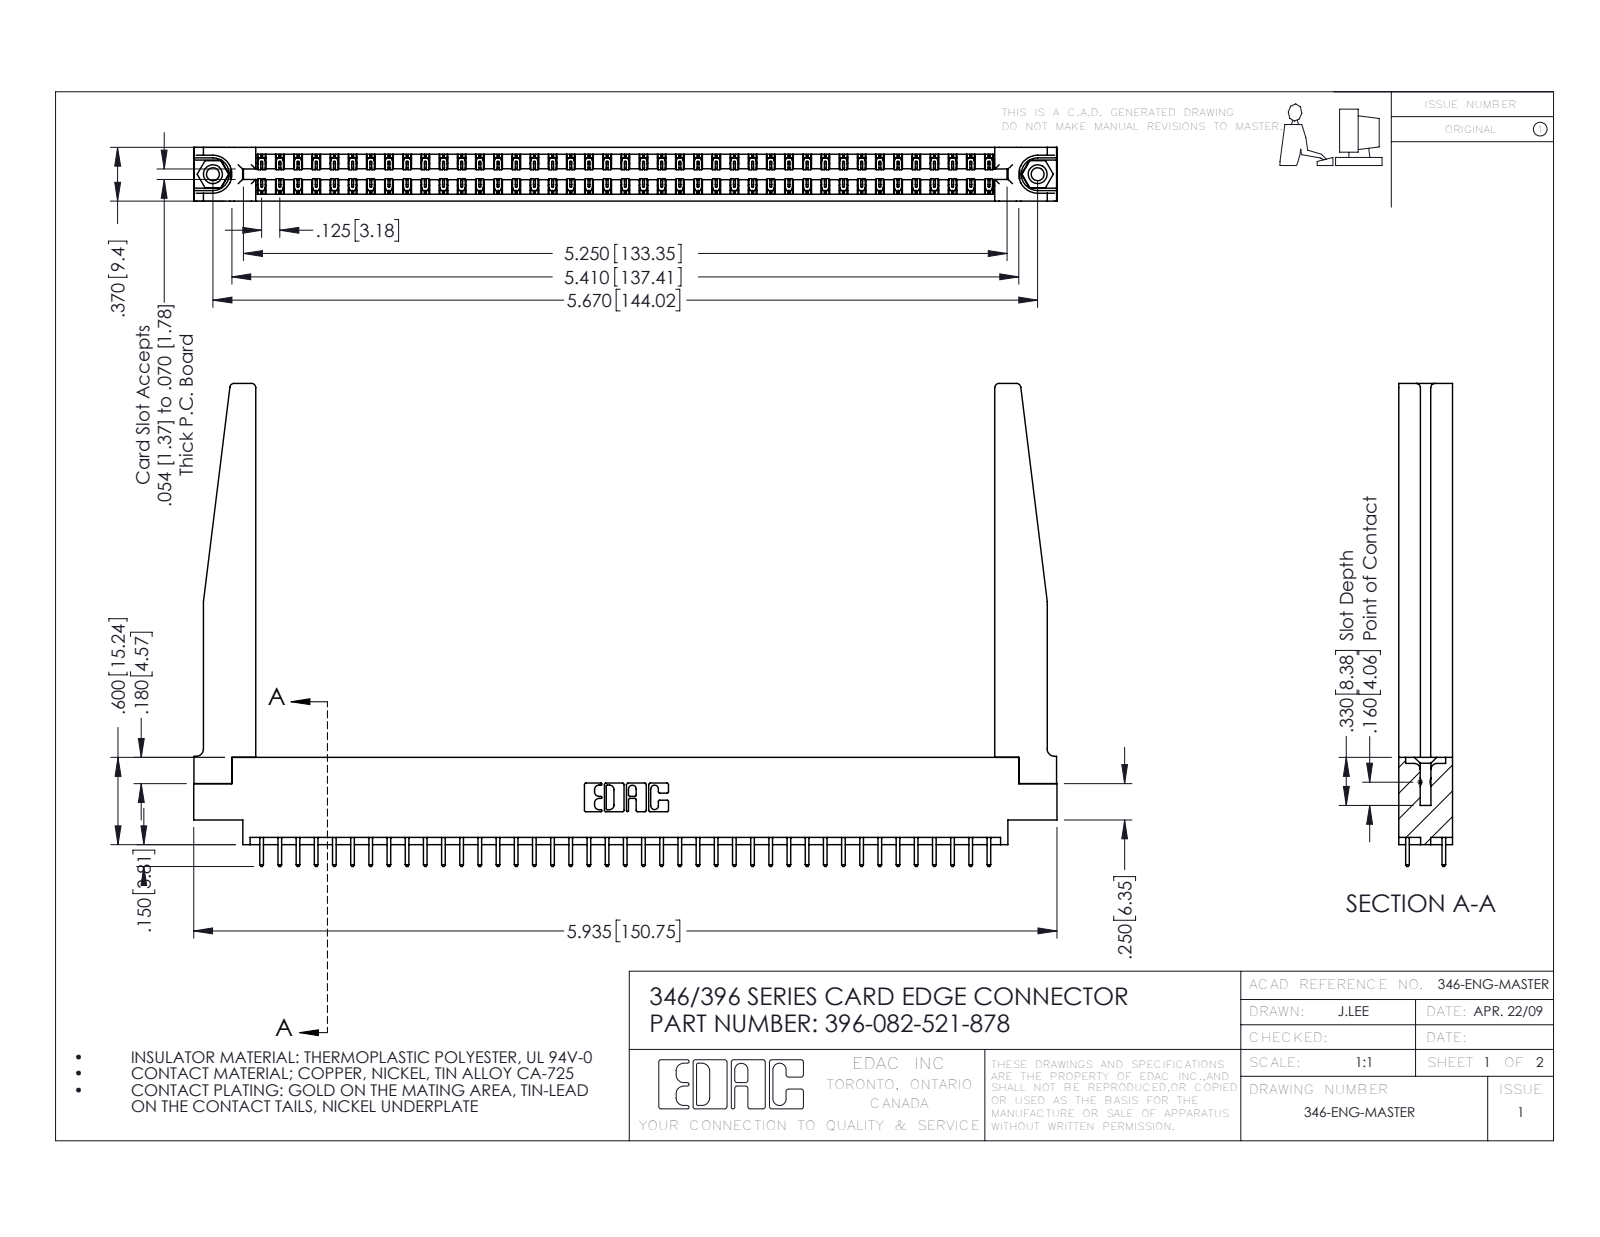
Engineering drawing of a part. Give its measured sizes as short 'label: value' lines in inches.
name: 345-250-001_345-250-001-102; 345-292-001_345-293-121; 346 Part_0.170 Offset - 0.156 Dia-TH; 396-082-521-878 (+1 more)
written by: SolidWorks 2016 (CONFIG_CONTROL_DESIGN)
unit: in
bodies: 87 solids, 4624 faces (3092 planar, 1480 cylindrical, 52 other)
size: 5.935 × 3.32 × 0.37
volume: 1.307 in³; area: 40.94 in²
holes: 2× ⌀0.089, 2× ⌀0.125, 2× ⌀0.156, 1× ⌀0.064
bosses: 2× ⌀0.155
rounds: 123× R0.006, 82× R0.01, 22× R0.01, 8× R0.03, 6× R0.007, 6× R0.031, 3× R0.026, 2× R0.014
face distances: 0.37, 0.048, 0.322, 0.072, 0.25, 0.15, 0.148, 0.298, 0.025, 0.275
hole spacings: 0.246, 5.461, 5.67
